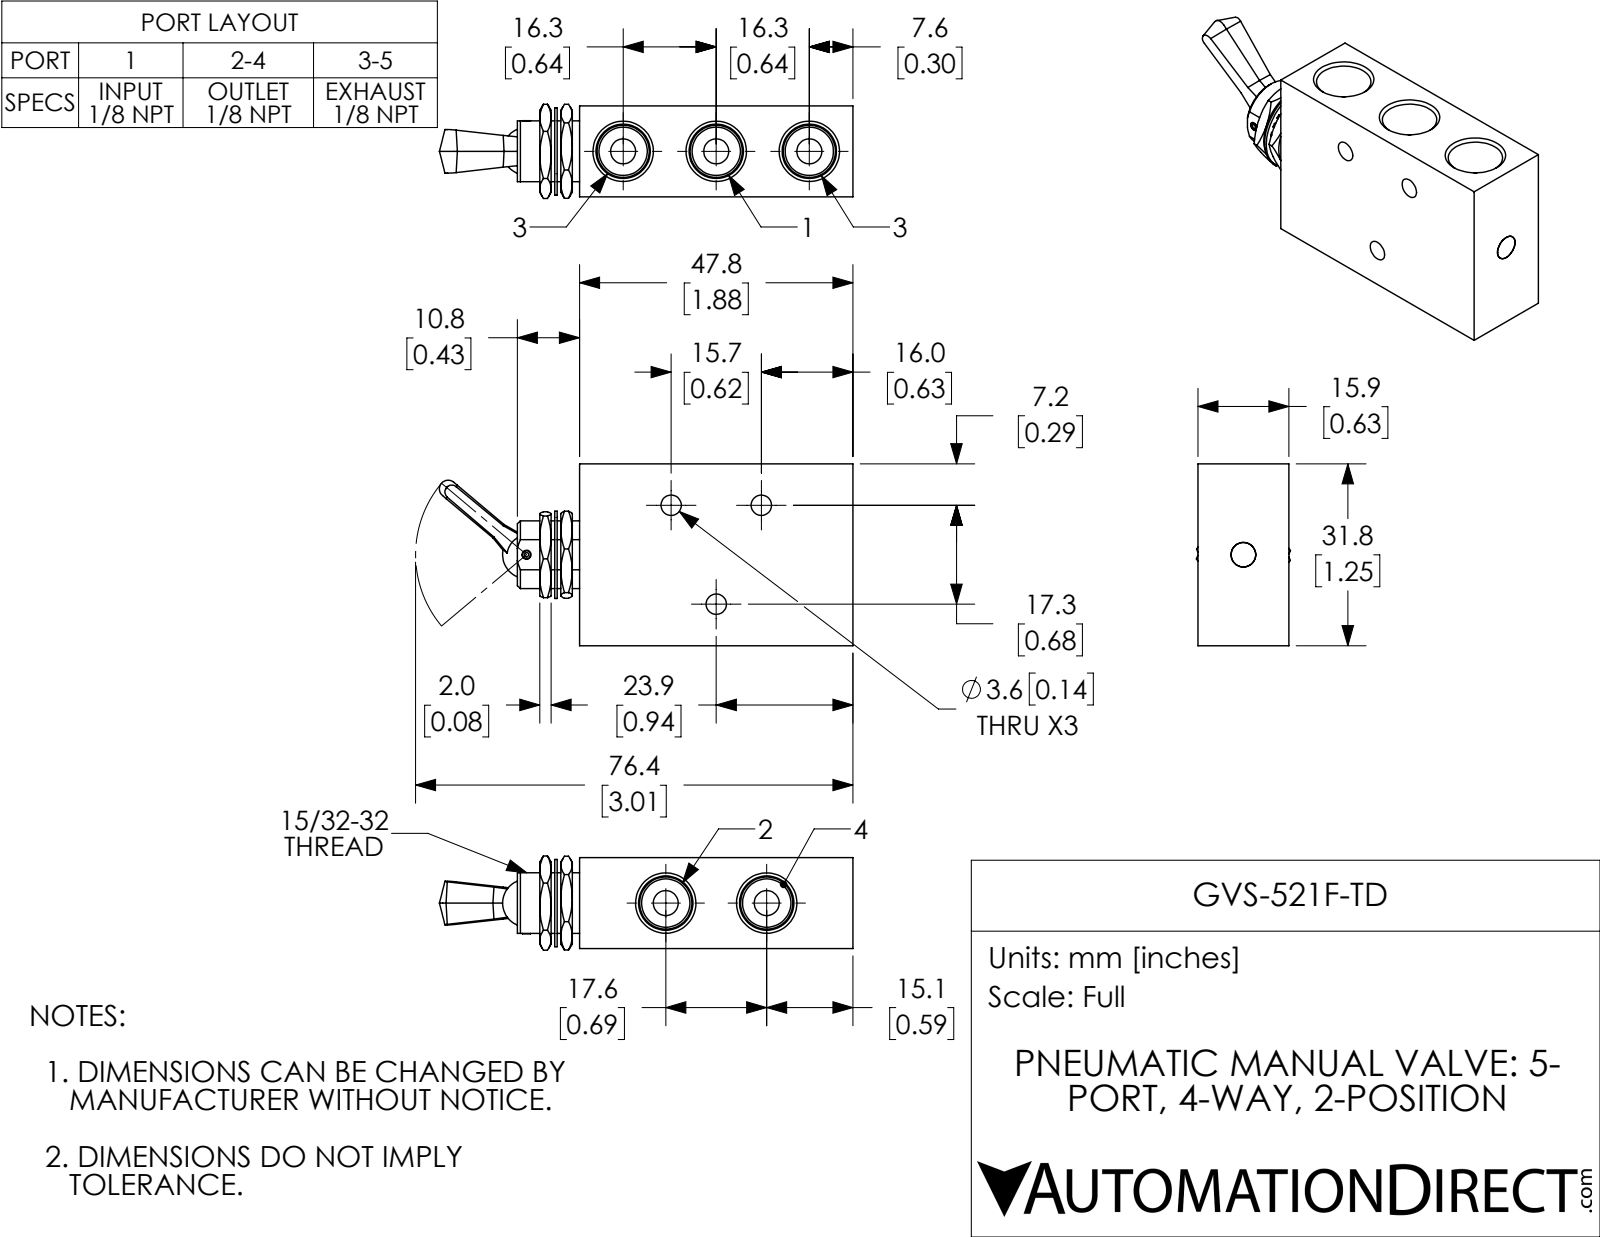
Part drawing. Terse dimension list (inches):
name: GVS-521F-TD
written by: SolidWorks 2018 (AUTOMOTIVE_DESIGN)
unit: in
bodies: 7 solids, 289 faces (110 planar, 111 cylindrical, 68 other)
size: 2.843 × 1.25 × 0.648
volume: 1.08 in³; area: 17.33 in²
holes: 6× ⌀0.332, 5× ⌀0.172, 3× ⌀0.14, 1× ⌀0.03, 1× ⌀0.062, 1× ⌀0.07, 1× ⌀0.169, 1× ⌀0.29, 1× ⌀0.415, 1× ⌀0.415, 1× ⌀0.438, 1× ⌀0.504
bosses: 1× ⌀0.6, 1× ⌀0.063
rounds: 1× R0.233, 1× R0.239, 1× R0.26
face distances: 0.625, 1.25, 1.88, 0.046, 1.834, 0.35, 0.9, 0.55, 0.12, 1.788
hole spacings: 0.293, 0.347, 0.64, 0.748, 0.987, 0.62, 0.694, 1.051
